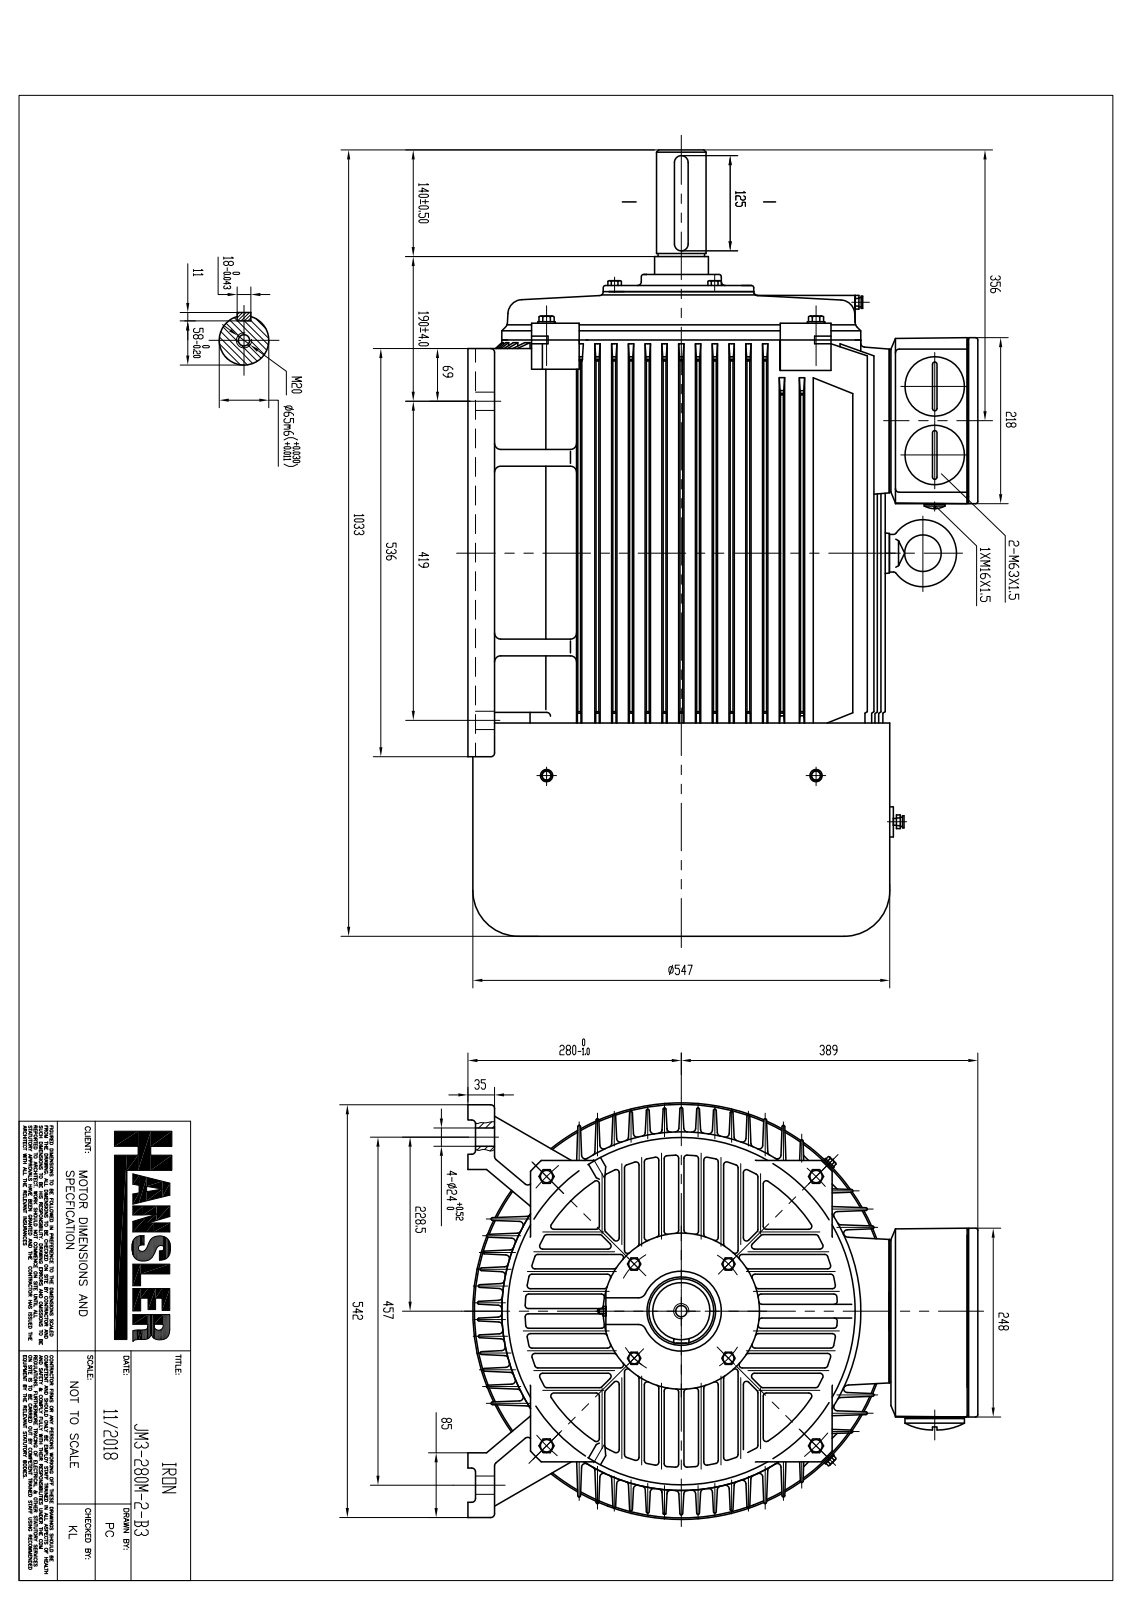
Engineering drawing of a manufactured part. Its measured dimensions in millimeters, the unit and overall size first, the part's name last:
Units: millimetres
Overall size (bounding box): 981.5 × 667.8 × 547
Round holes (diameter × count): ⌀10 ×10, ⌀12 ×5, ⌀24 ×5, ⌀8 ×4, ⌀8.39 ×4, ⌀8.4 ×4, ⌀11.2 ×4, ⌀12.55 ×4, ⌀12.6 ×4, ⌀14 ×4, ⌀14.5 ×4, ⌀43.31 ×2
Round bosses / shafts (diameter × count): ⌀18.75 ×4, ⌀16 ×4, ⌀12.59 ×4, ⌀12 ×4, ⌀10.86 ×4, ⌀10 ×4, ⌀9.03 ×4, ⌀8 ×4
Partial cylindrical surfaces — rounded edges, fillets, slot ends (radius × count): R4 ×160, R6 ×72, R5 ×36, R2 ×28, R10 ×18, R1 ×12, R8 ×8, R3 ×6
Main face-to-face distances: 57.13, 617.13, 6, 653, 560, 2, 10, 6.37, 63.5, 623.5
Hole centre spacings: 87.5, 175, 264.87, 337.5, 123.74, 123.75, 152, 162.49
Volume: 37 930 000 mm³ · Surface area: 7 735 000 mm²
Bodies: 58 solids, 6921 faces (4603 planar, 1140 cylindrical, 1178 other)
Part name (STEP PRODUCT): pc0534AA92lz1c
STEP written by: SIEMENS PLM Software NX 8.5 (AUTOMOTIVE_DESIGN)
